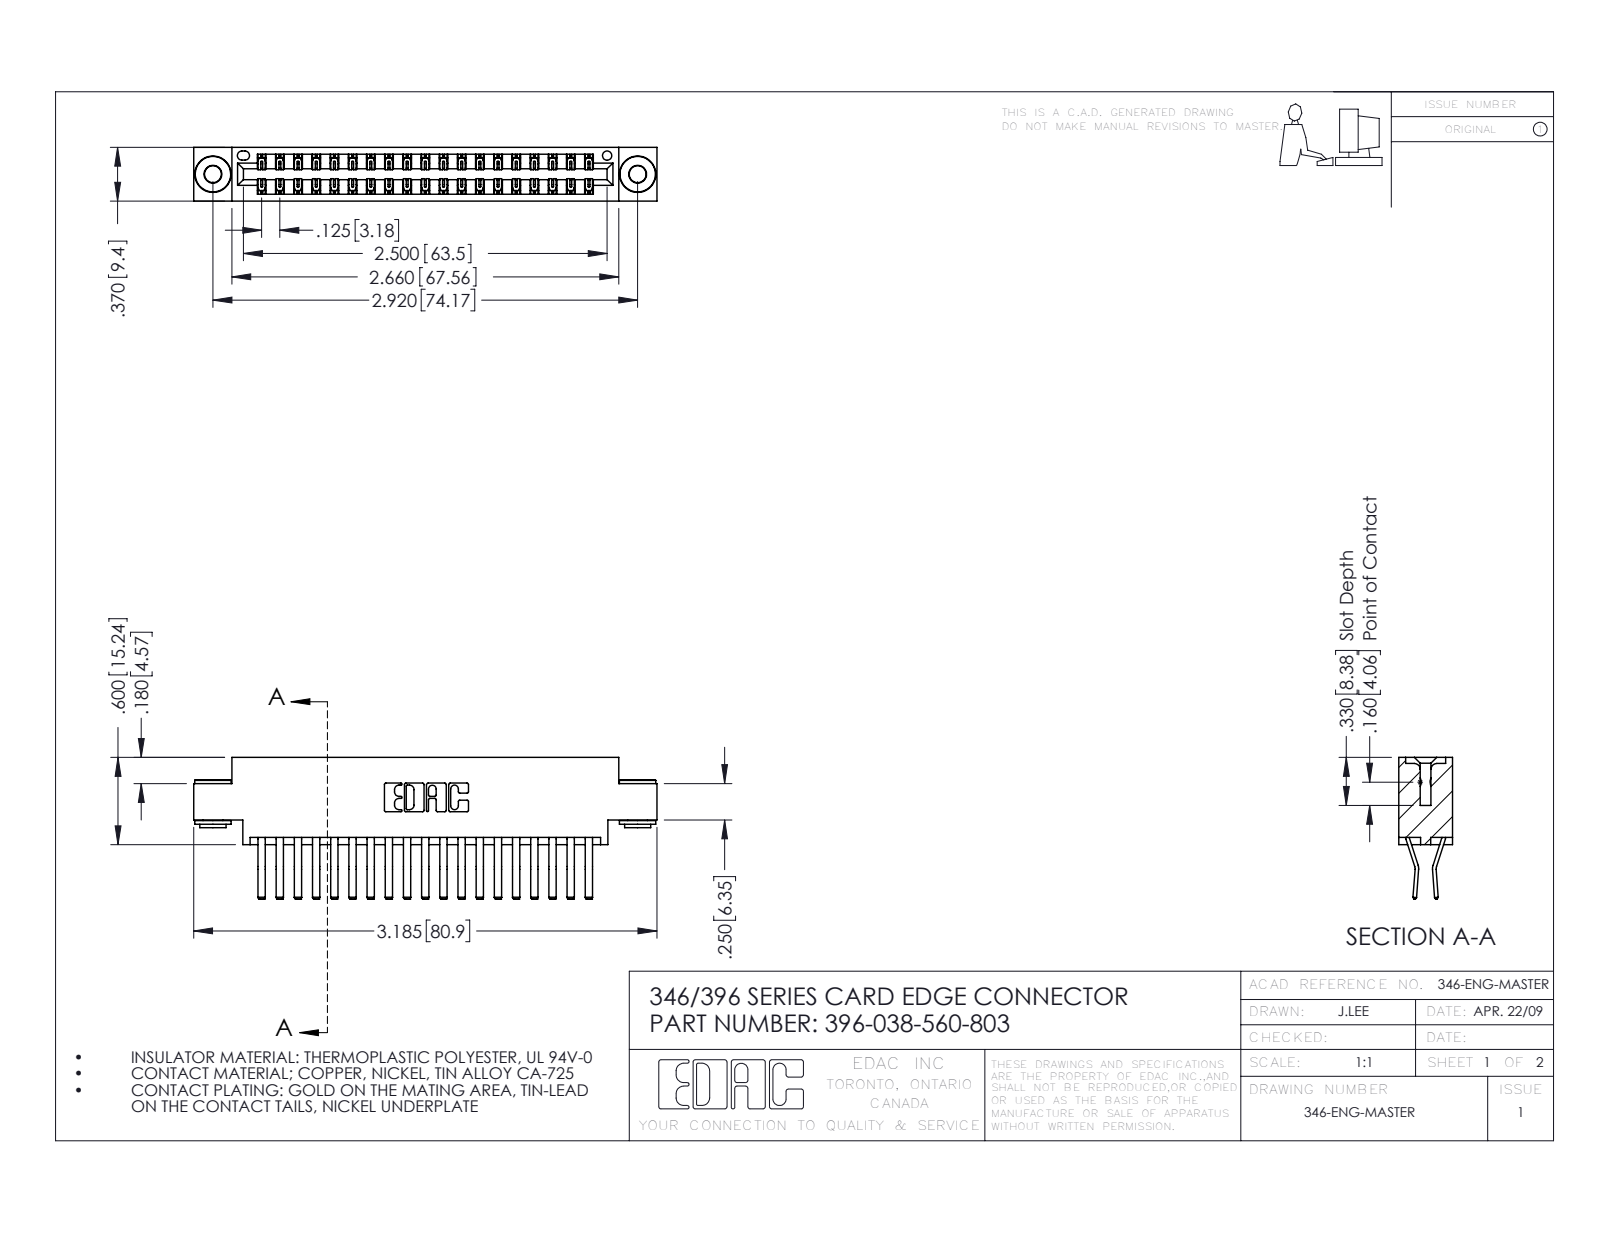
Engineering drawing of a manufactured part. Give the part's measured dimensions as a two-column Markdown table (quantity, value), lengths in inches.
| quantity | value |
| --- | --- |
| part name | 345-292-001_560 Tail; 345-250-002_345-250-002-102; 346 Part_0.170 Offset - 0.156 Dia-TH; 396-038-560-803 |
| STEP written by | SolidWorks 2016 (CONFIG_CONTROL_DESIGN) |
| units | inches |
| bodies | 41 solids, 2216 faces (1420 planar, 788 cylindrical, 8 other) |
| overall size | 3.185 × 0.975 × 0.37 |
| volume | 0.477 in³ |
| surface area | 17.75 in² |
| round holes (diameter × count) | 0.116 × 2, 0.156 × 2, 0.064 × 1 |
| round bosses / shafts (diameter × count) | 0.25 × 2, 0.18 × 2, 0.136 × 2 |
| partial cylindrical surfaces (radius × count) | 0.006 × 57, 0.01 × 22, 0.007 × 6, 0.031 × 6, 0.026 × 3, 0.01 × 2, 0.014 × 2, 0.022 × 2 |
| main face-to-face distances | 0.048, 0.322, 0.37, 0.25, 0.025, 0.275, 0.072, 0.298, 0.148, 0.222 |
| hole center spacings | 0.246, 2.713, 2.92 |
